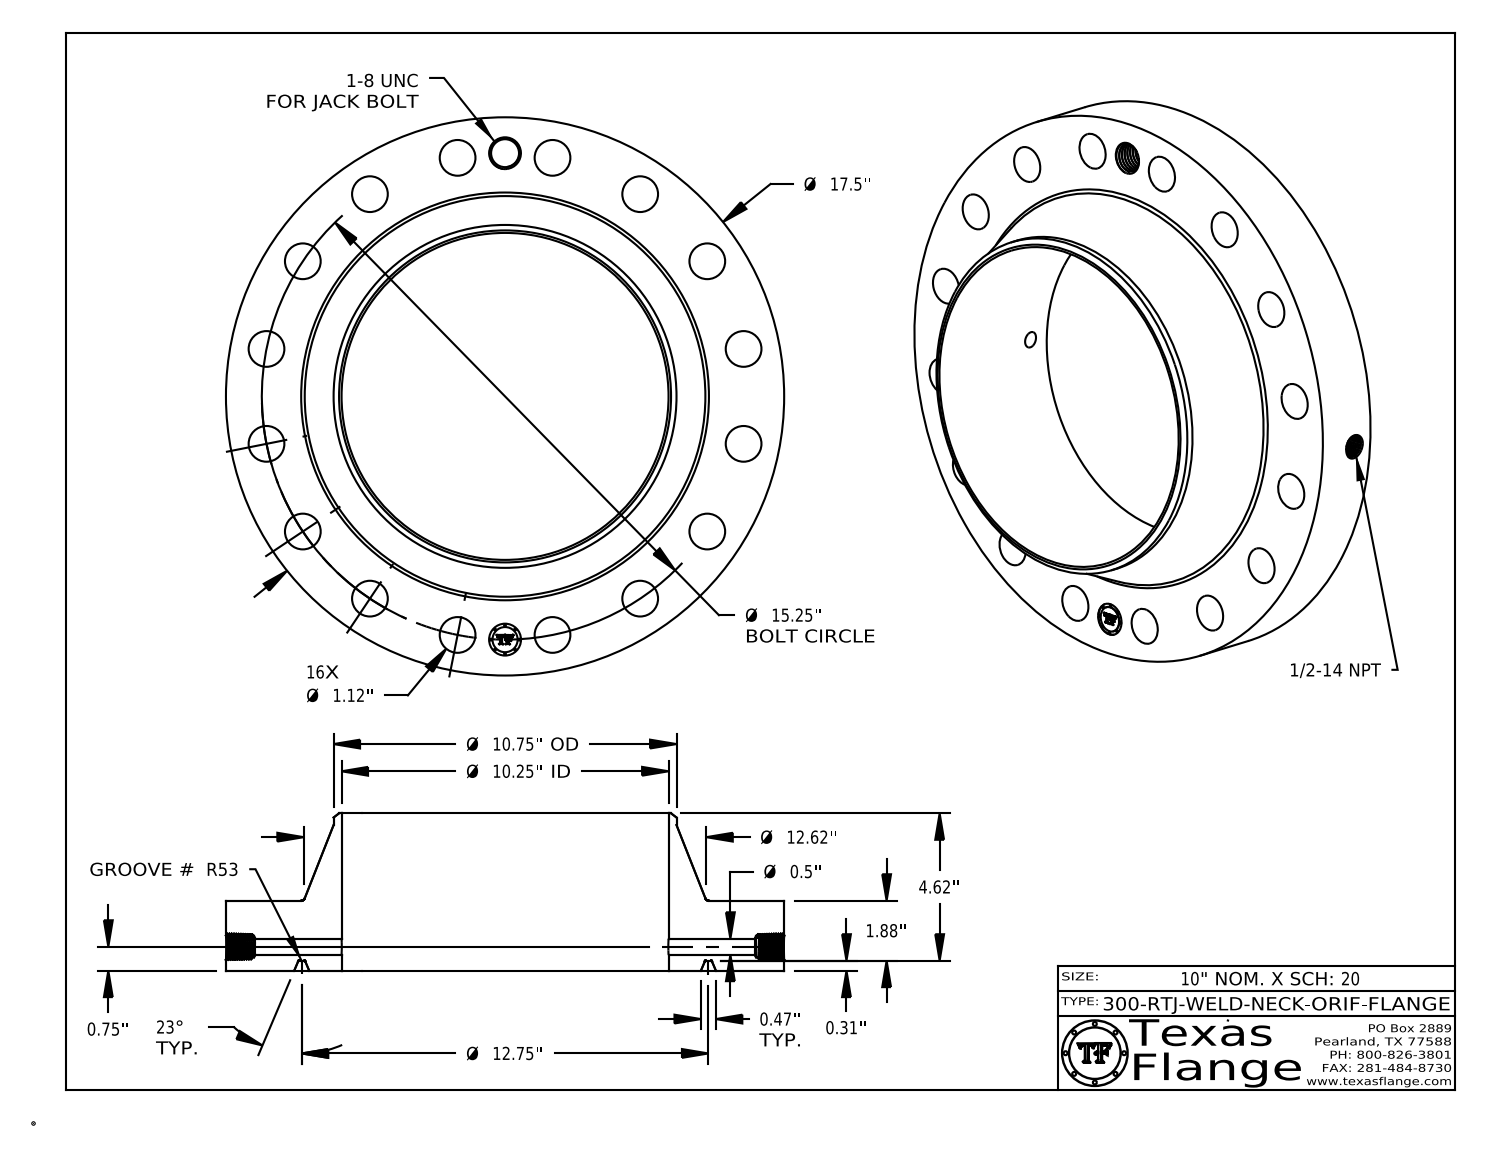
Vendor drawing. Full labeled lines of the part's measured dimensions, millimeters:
Part name (STEP PRODUCT): 300-RTJ-WELD-NECK
STEP written by: CATIA V5 STEP AP214 (AUTOMOTIVE_DESIGN)
Units: millimetres
Bodies: 1 solid, 809 faces (370 planar, 112 cylindrical, 327 other)
Overall size (bounding box): 444.5 × 444.5 × 125.3
Volume: 6 003 000 mm³ · Surface area: 512 400 mm²
Round holes (diameter × count): ⌀28.4 ×16, ⌀12.7 ×1, ⌀17.1 ×1, ⌀22.2 ×1, ⌀25.4 ×1, ⌀260.4 ×1
Round bosses / shafts (diameter × count): ⌀1.5 ×8, ⌀444.5 ×1, ⌀273.1 ×1, ⌀20 ×1
Main face-to-face distances: 55.7, 8, 47.8, 125.3, 117.3, 69.6, 0.4, 55.3, 47.4, 70
Hole centre spacings: 148.2, 193.7, 273.9, 357.9, 379.9, 75.6, 75.6, 215.2
